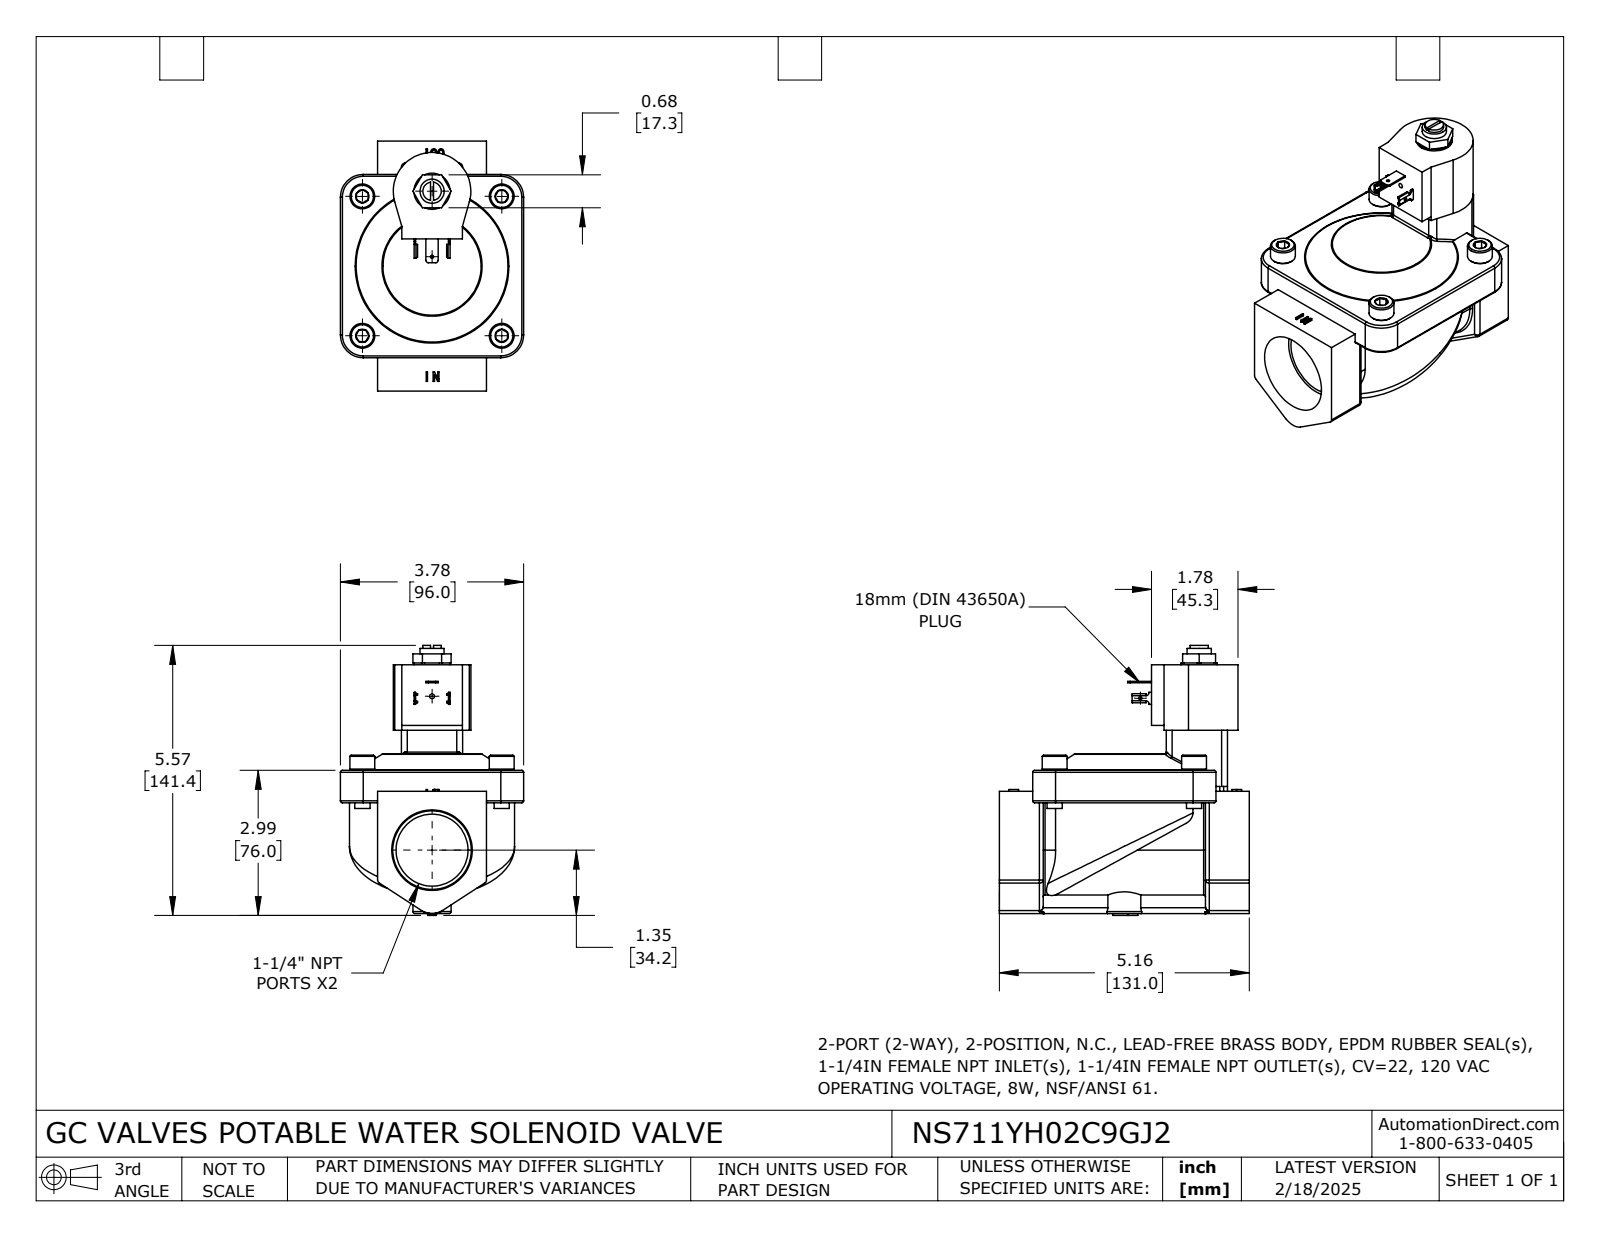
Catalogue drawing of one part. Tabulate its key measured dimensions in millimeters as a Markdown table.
| quantity | value |
| --- | --- |
| part name | NS711YH02C9GJ2 |
| STEP written by | SolidWorks 2024 (CONFIG_CONTROL_DESIGN) |
| units | millimeters |
| bodies | 1 solid, 442 faces (201 planar, 115 cylindrical, 126 other) |
| overall size | 141.37 × 131 × 96 |
| volume | 569 832 mm³ |
| surface area | 69 550 mm² |
| round holes (diameter × count) | 1.68 × 1, 1.7 × 1, 2.53 × 1, 30.48 × 1, 37.69 × 1 |
| round bosses / shafts (diameter × count) | 13 × 4, 8 × 4, 18.95 × 1, 12.67 × 1, 9.65 × 1 |
| partial cylindrical surfaces (radius × count) | 2 × 14, 1 × 13, 3 × 6, 0.15 × 4, 1.04 × 4, 12 × 4, 0.2 × 2, 1.27 × 2 |
| main face-to-face distances | 19.5, 32, 11, 6, 76.5, 8.5, 96, 17, 25.5, 12.5 |
| hole center spacings | 34.29, 80.56 |
